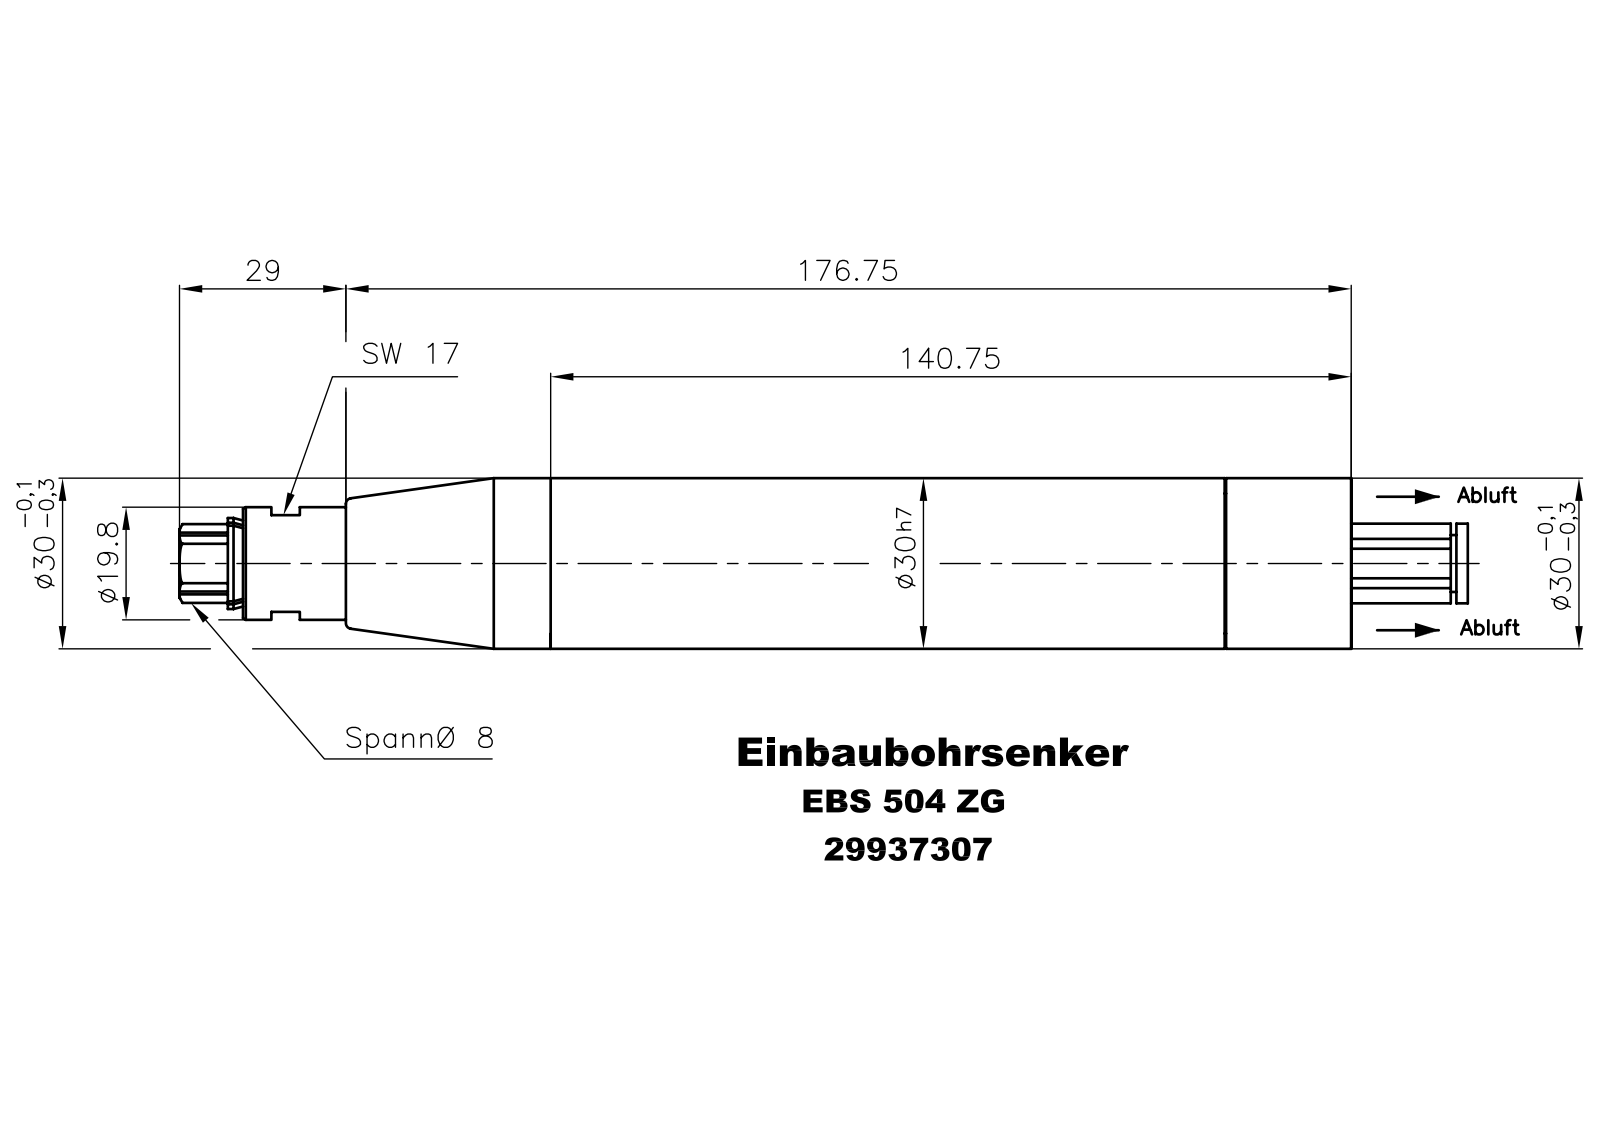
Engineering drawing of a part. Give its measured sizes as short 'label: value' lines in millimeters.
name: Bauteil7
written by: Autodesk Inventor 2008 (AUTOMOTIVE_DESIGN)
unit: mm
bodies: 1 solid, 162 faces (88 planar, 42 cylindrical, 32 other)
size: 228.16 × 30 × 30
volume: 127 054 mm³; area: 22 981 mm²
holes: 1× ⌀8, 1× ⌀8.5, 1× ⌀10, 1× ⌀12.1, 1× ⌀28
bosses: 1× ⌀30, 1× ⌀27.24, 1× ⌀19.8, 1× ⌀16, 1× ⌀13, 1× ⌀12, 1× ⌀9.2
rounds: 3× R22.5, 1× R5.6, 1× R6.75, 1× R7.25, 1× R11.24, 1× R11.25
face distances: 3.5, 20.5, 22, 24, 12, 18, 196.3, 174.3, 142.3, 120.3
